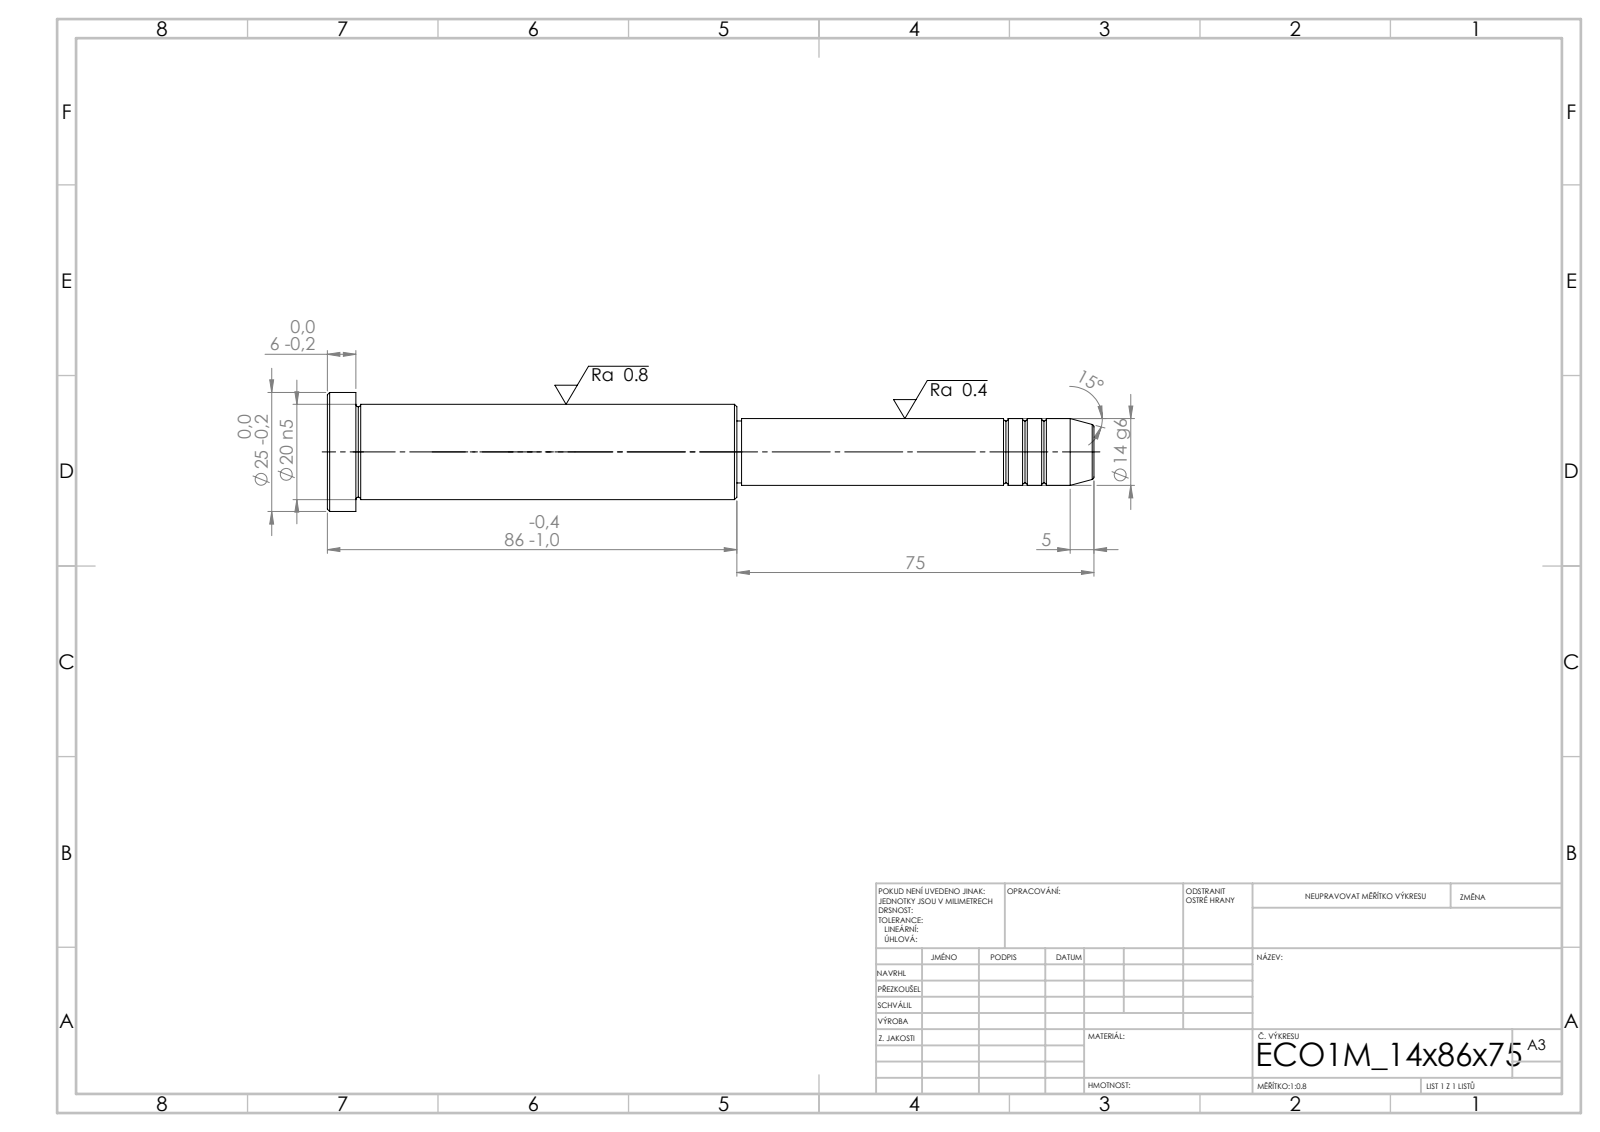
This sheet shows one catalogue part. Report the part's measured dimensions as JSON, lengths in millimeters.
{"step_written_by": "SolidWorks 2019 (CONFIG_CONTROL_DESIGN)", "units": "millimeters", "bodies": {"solids": 1, "faces": 43, "planar": 5, "cylindrical": 14, "other": 24}, "overall_size": [161, 25, 25], "volume_mm3": 39371, "surface_area_mm2": 9803, "round_bosses_or_shafts": [[25, 1], [20, 1], [14, 1], [13, 1]], "face_to_face_distances": [6, 80, 86, 75, 155, 161, 74, 1, 81, 87]}
